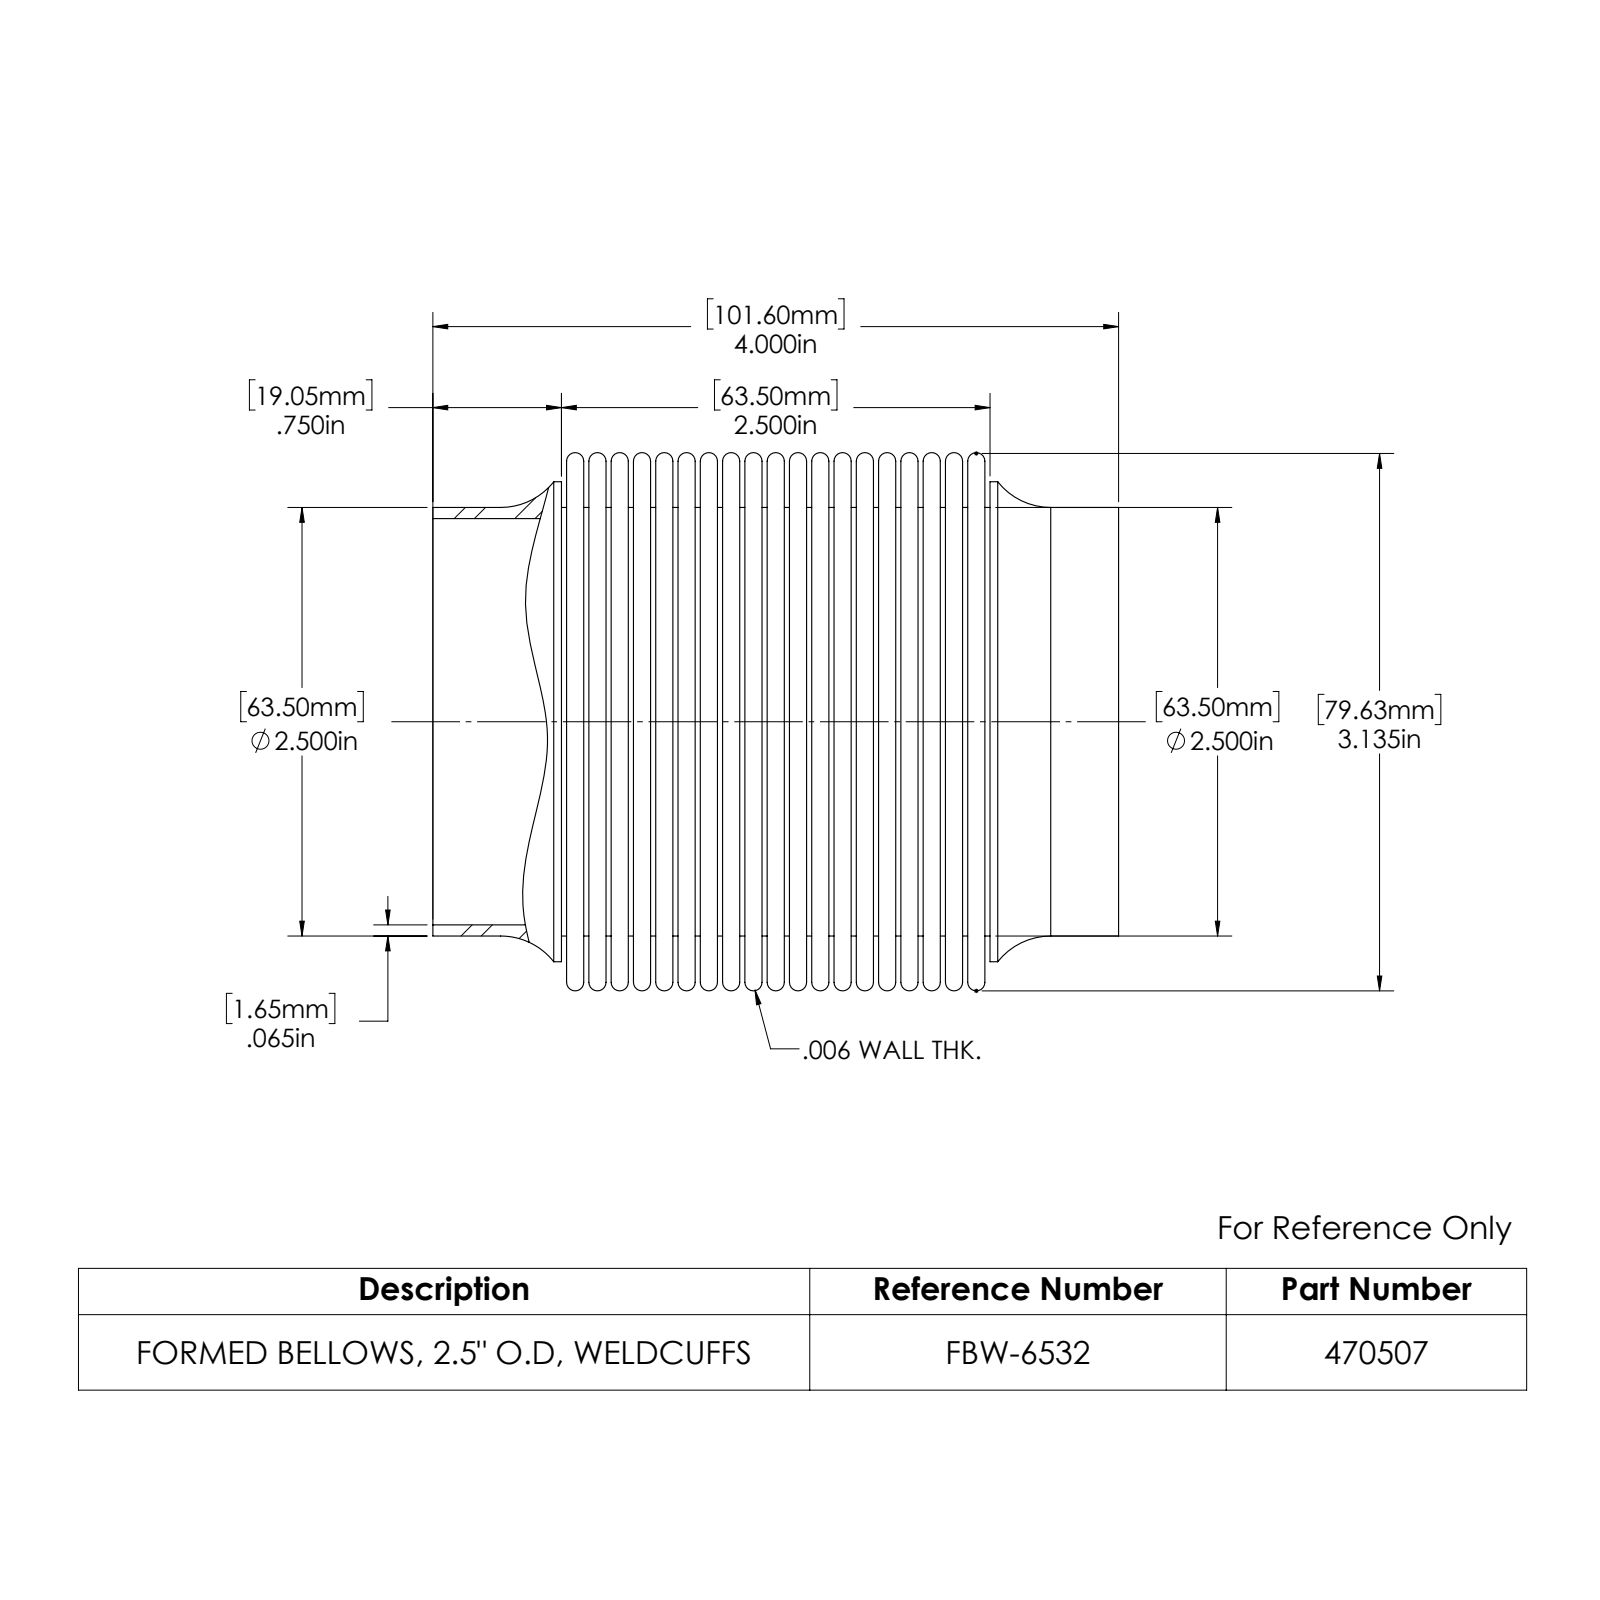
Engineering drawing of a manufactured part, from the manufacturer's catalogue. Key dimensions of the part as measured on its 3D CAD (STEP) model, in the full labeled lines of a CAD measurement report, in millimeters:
Part name (STEP PRODUCT): 470507
STEP written by: SolidWorks 2022 (AUTOMOTIVE_DESIGN)
Units: millimetres
Bodies: 1 solid, 266 faces (86 planar, 100 cylindrical, 80 other)
Overall size (bounding box): 101.6 × 79.8 × 79.8
Volume: 26 470 mm³ · Surface area: 181 100 mm²
Round holes (diameter × count): ⌀60.2 ×1, ⌀63.2 ×1, ⌀70.9 ×1
Round bosses / shafts (diameter × count): ⌀71.1 ×1, ⌀63.5 ×1
Main face-to-face distances: 3.3, 16.5, 6.6, 19.8, 13.2, 9.9, 23.1, 33, 9.9, 36.3
